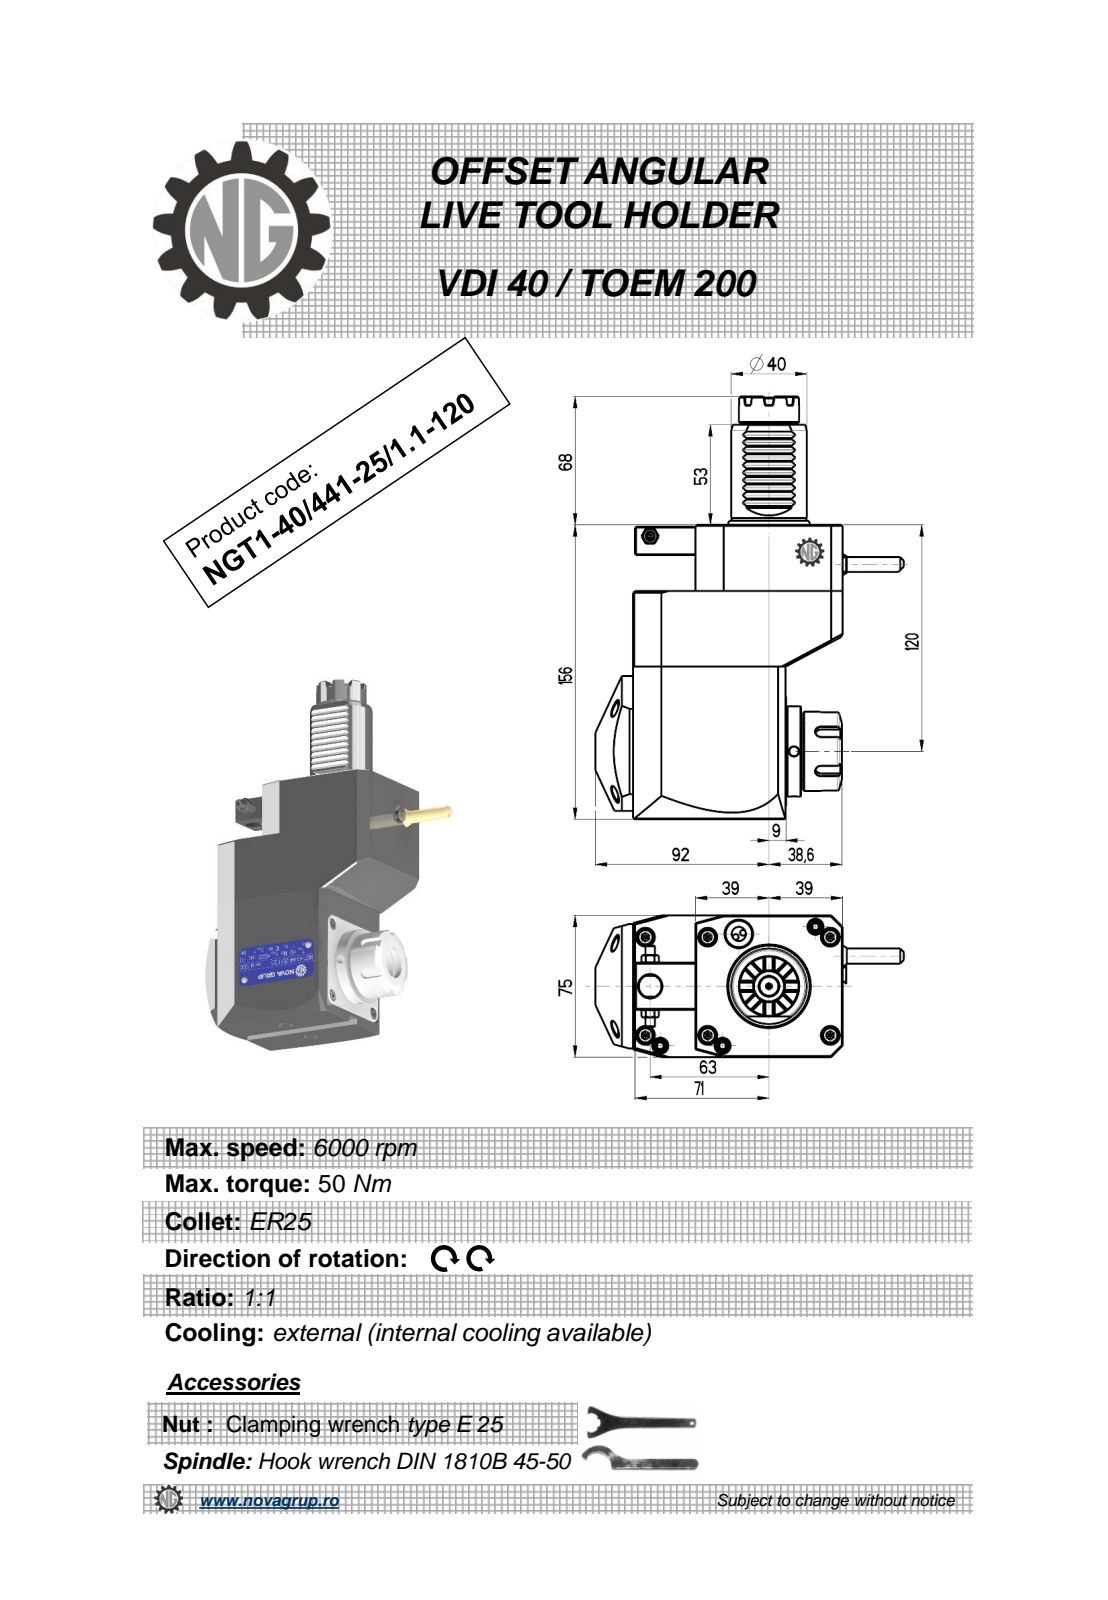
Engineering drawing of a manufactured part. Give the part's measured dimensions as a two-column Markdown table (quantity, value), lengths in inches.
| quantity | value |
| --- | --- |
| part name | NGT1_40_441_25_1_1_120 |
| STEP written by | PRO/ENGINEER BY PARAMETRIC TECHNOLOGY CORPORATION, 2010280 (CONFIG_CONTROL_DESIGN) |
| units | inches |
| bodies | 1 solid, 523 faces (240 planar, 94 cylindrical, 189 other) |
| overall size | 8.819 × 6.437 × 3.016 |
| volume | 71.58 in³ |
| surface area | 136.9 in² |
| round holes (diameter × count) | 0.197 × 3, 0.118 × 1, 0.374 × 1, 0.472 × 1, 0.799 × 1 |
| round bosses / shafts (diameter × count) | 1.89 × 1, 1.654 × 1, 1.575 × 1, 1.476 × 1, 1.299 × 1, 1.26 × 1, 0.669 × 1, 0.394 × 1 |
| partial cylindrical surfaces (radius × count) | 0.01 × 12, 0.012 × 10, 0.008 × 6, 0.118 × 5, 0.02 × 1, 0.339 × 1, 1.575 × 1 |
| main face-to-face distances | 2.953, 6.142, 4.37, 1.181, 1.378, 4.764, 3.189, 1.299, 3.071, 1.89 |
| hole center spacings | 0.824, 3.002, 3.948, 4.429 |
